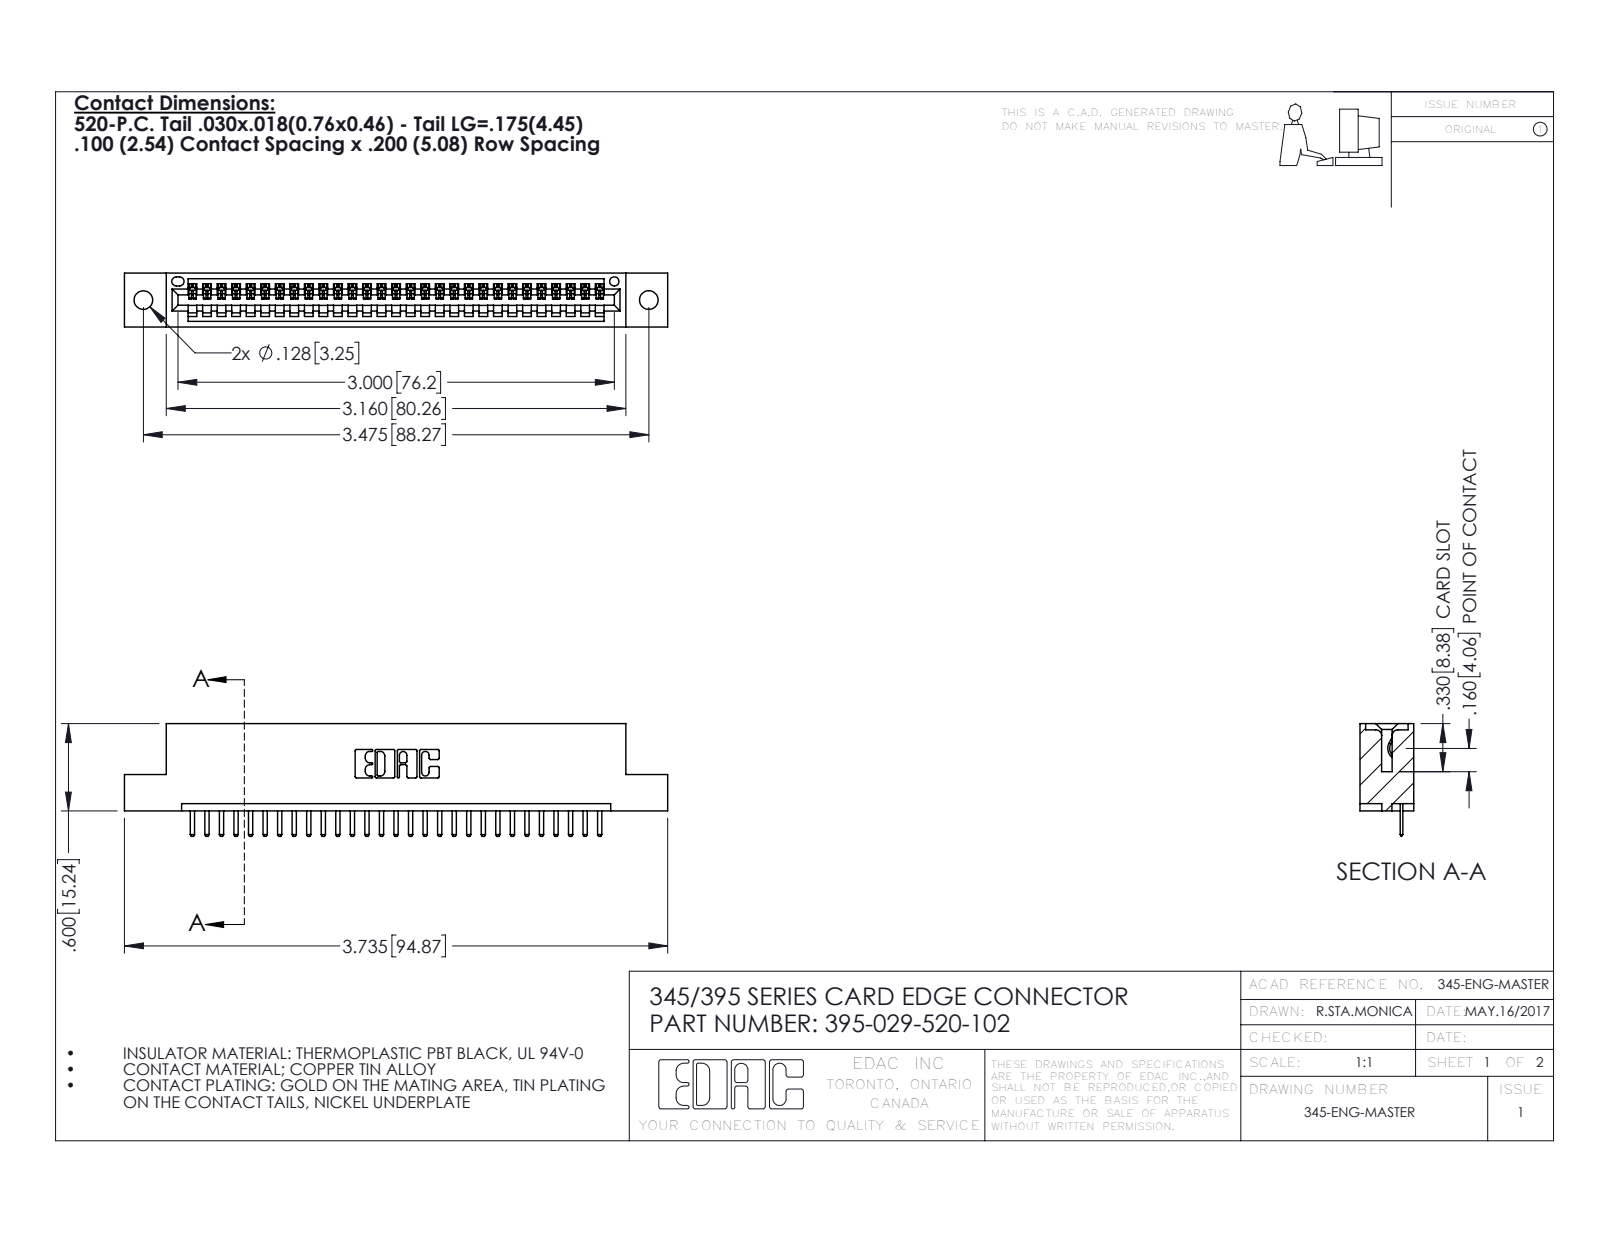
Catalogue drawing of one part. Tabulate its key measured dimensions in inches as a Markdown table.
| quantity | value |
| --- | --- |
| part name | 345-292-001_345-293-120; 395-029-520-102; 345 Part_Flush Mounting Lugs - 0.128 Dia |
| STEP written by | SolidWorks 2016 (CONFIG_CONTROL_DESIGN) |
| units | inches |
| bodies | 30 solids, 1924 faces (1298 planar, 626 cylindrical, 0 other) |
| overall size | 3.735 × 0.775 × 0.37 |
| volume | 0.536 in³ |
| surface area | 16.98 in² |
| round holes (diameter × count) | 0.128 × 2, 0.064 × 1 |
| partial cylindrical surfaces (radius × count) | 0.01 × 60, 0.006 × 58, 0.01 × 22, 0.007 × 6, 0.031 × 6, 0.026 × 3, 0.031 × 2, 0.04 × 2 |
| main face-to-face distances | 0.298, 0.072, 0.37, 0.2, 0.098, 0.272, 0.025, 0.225, 0.072, 0.149 |
| hole center spacings | 0.27, 3.24, 3.475 |
